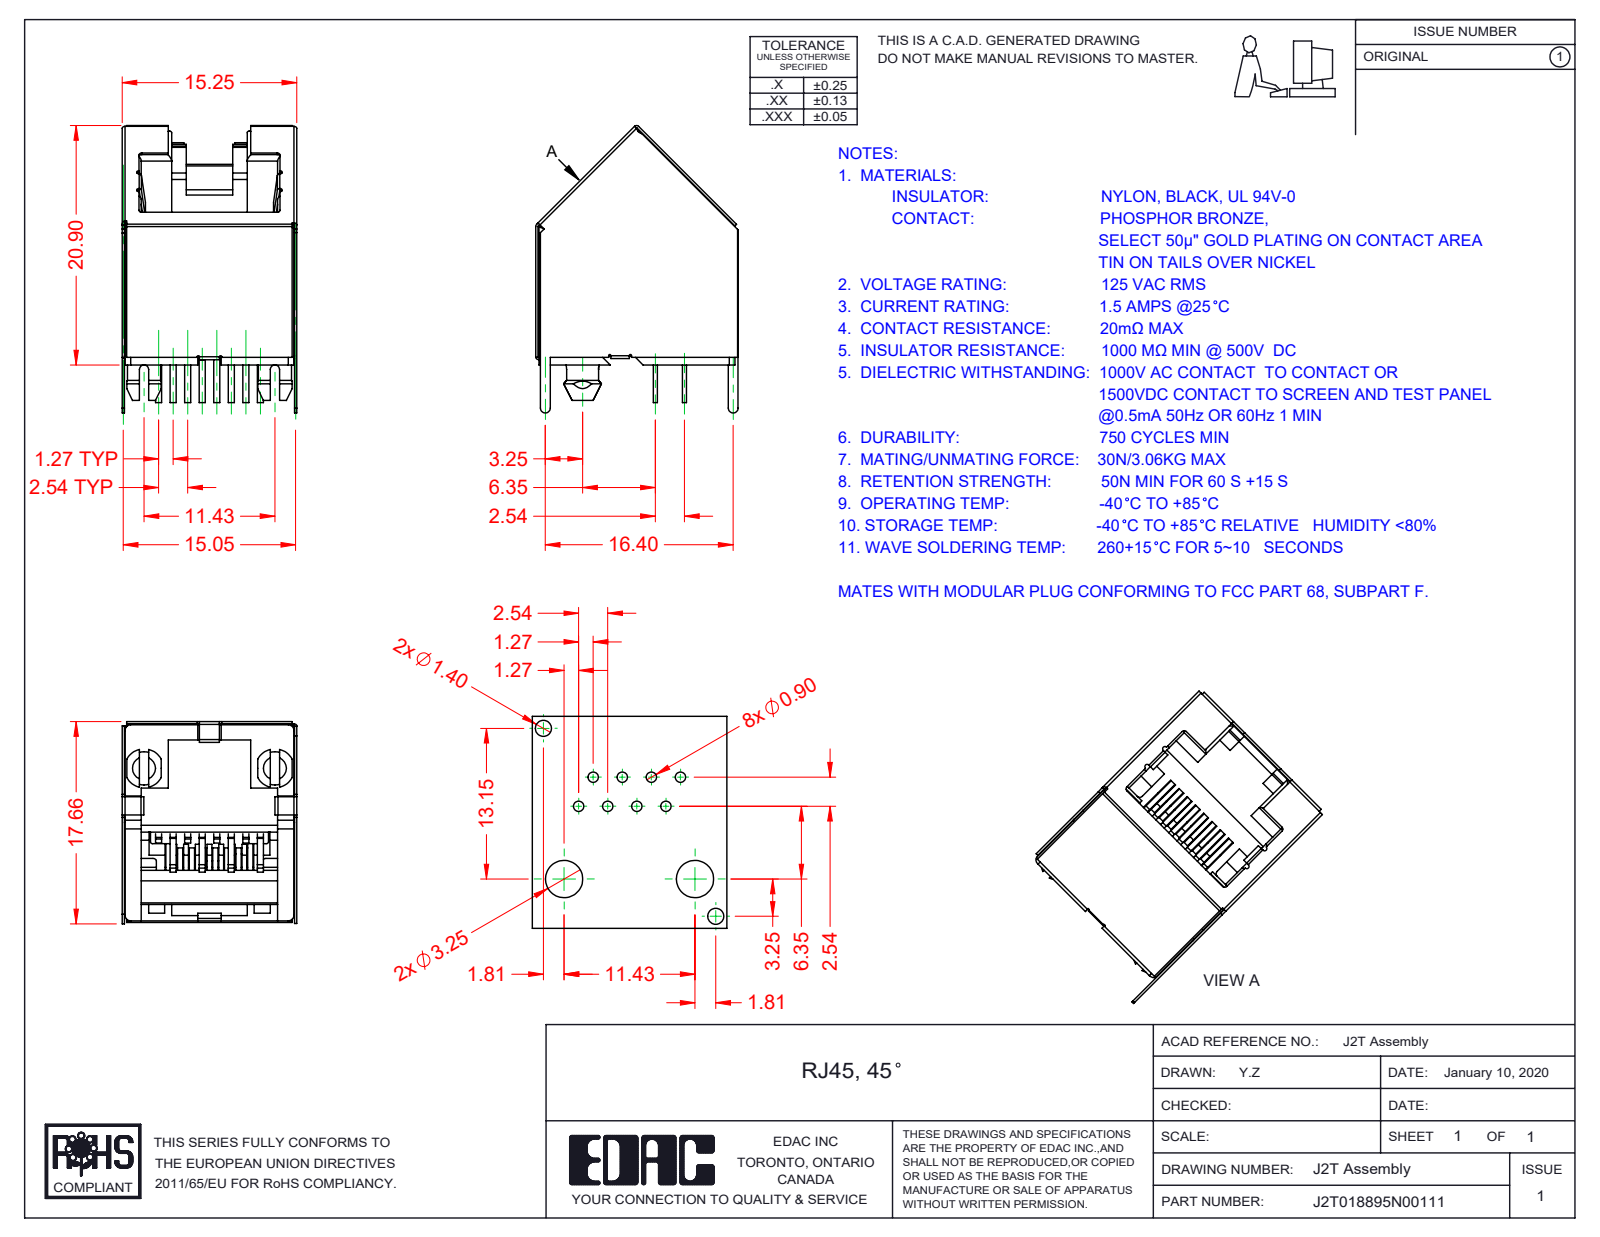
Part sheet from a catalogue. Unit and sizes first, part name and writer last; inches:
Units: inches
Overall size (bounding box): 0.988 × 0.695 × 0.6
Round bosses / shafts (diameter × count): ⌀0.114 ×2
Partial cylindrical surfaces — rounded edges, fillets, slot ends (radius × count): R0.02 ×21, R0.039 ×16, R0.008 ×12, R0.01 ×10, R0.057 ×8, R0.06 ×8, R0.004 ×5, R0.012 ×3
Main face-to-face distances: 0.592, 0.056, 0.525, 0.583, 0.591, 0.6, 0.584, 0.59, 0.582, 0.581
Volume: 0.12 in³ · Surface area: 8.026 in²
Bodies: 11 solids, 631 faces (447 planar, 161 cylindrical, 23 other)
Part name (STEP PRODUCT): RJ2T018895N00111; 2T Contact Lock; 2T Contacts; 2T Shell (+1 more)
STEP written by: SolidWorks 2016 (CONFIG_CONTROL_DESIGN)
